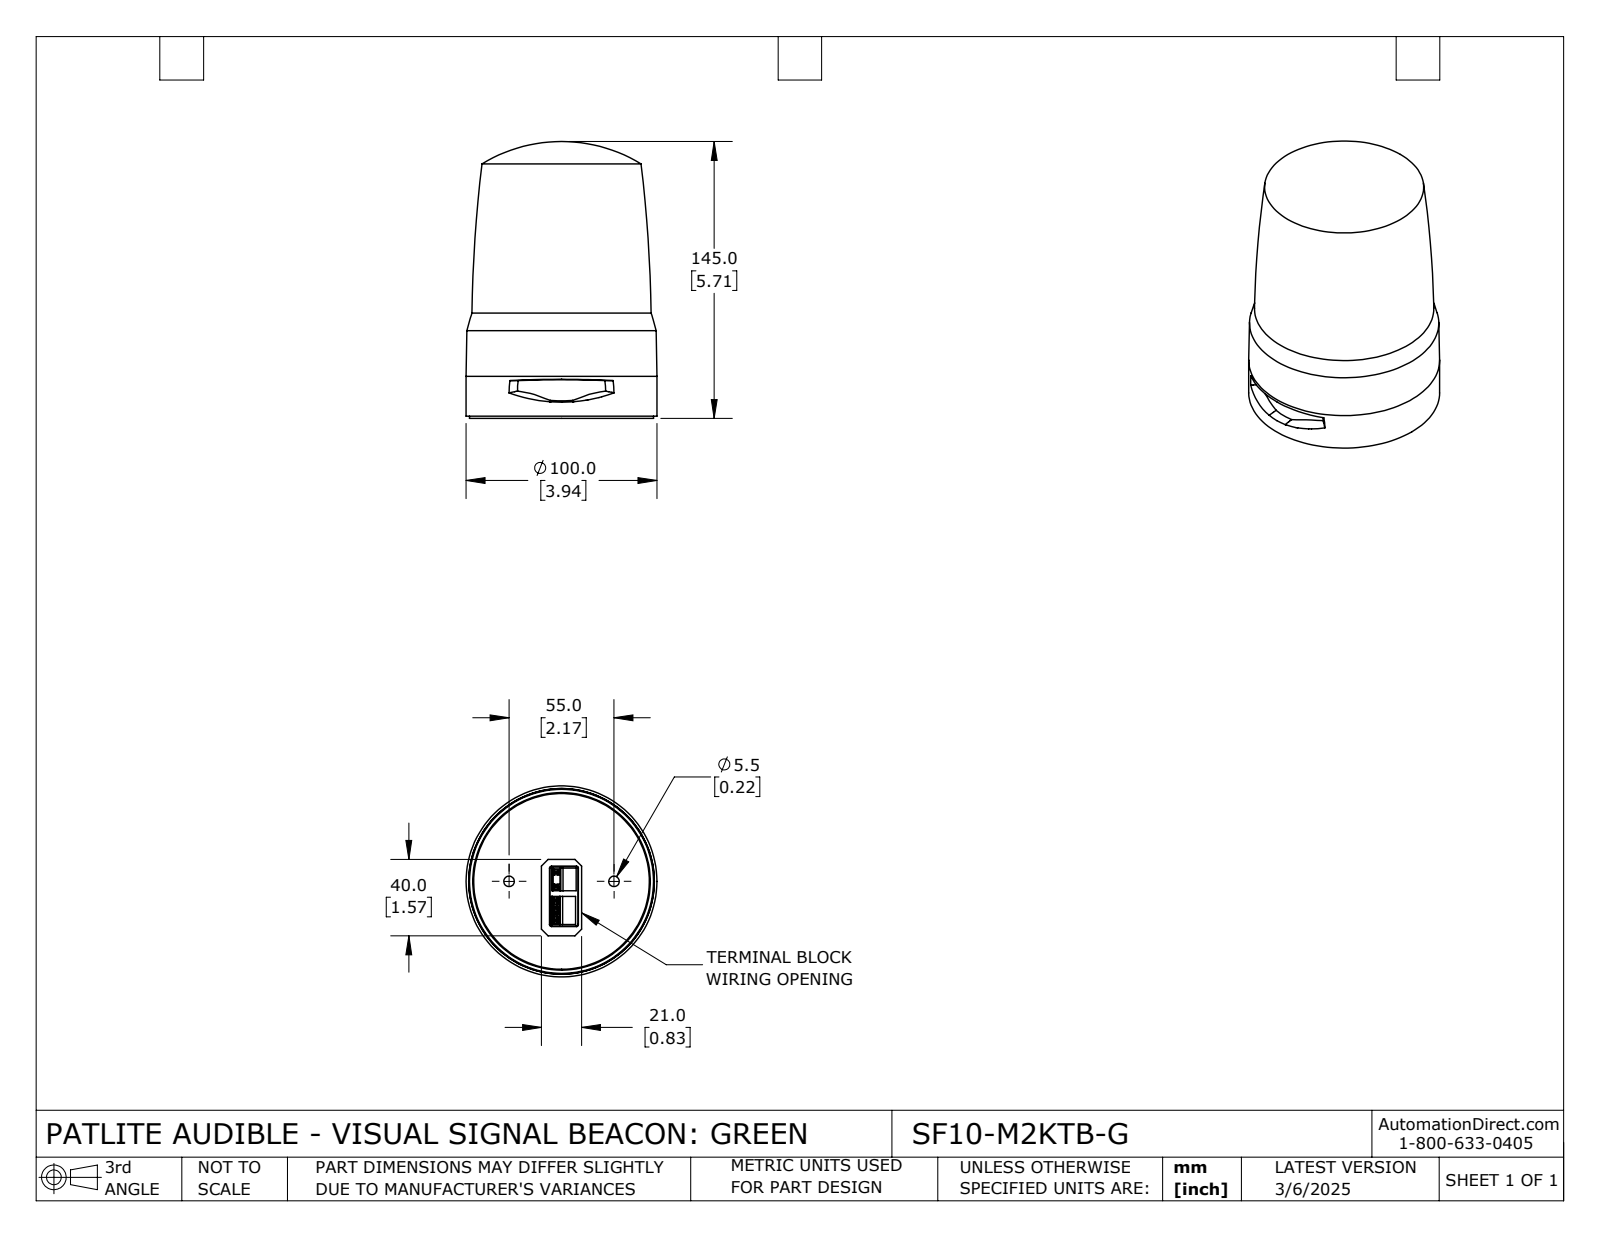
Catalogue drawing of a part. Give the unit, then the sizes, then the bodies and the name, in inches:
Units: inches
Overall size (bounding box): 5.709 × 3.937 × 3.937
Round holes (diameter × count): ⌀0.217 ×2, ⌀0.512 ×2, ⌀3.661 ×1
Round bosses / shafts (diameter × count): ⌀3.937 ×1, ⌀3.795 ×1, ⌀3.72 ×1, ⌀3.669 ×1, ⌀3.622 ×1
Partial cylindrical surfaces — rounded edges, fillets, slot ends (radius × count): R0.039 ×4, R0.012 ×2, R1.762 ×1, R1.772 ×1
Main face-to-face distances: 0.248, 0.717, 0.469, 0.22, 0.496, 0.201, 0.016, 0.185, 0.047, 0.669
Hole centre spacings: 1.083, 2.165
Volume: 53.41 in³ · Surface area: 123.8 in²
Bodies: 2 solids, 275 faces (174 planar, 31 cylindrical, 70 other)
Part name (STEP PRODUCT): SF10-M2KTB-G
STEP written by: SolidWorks 2024 (CONFIG_CONTROL_DESIGN)
